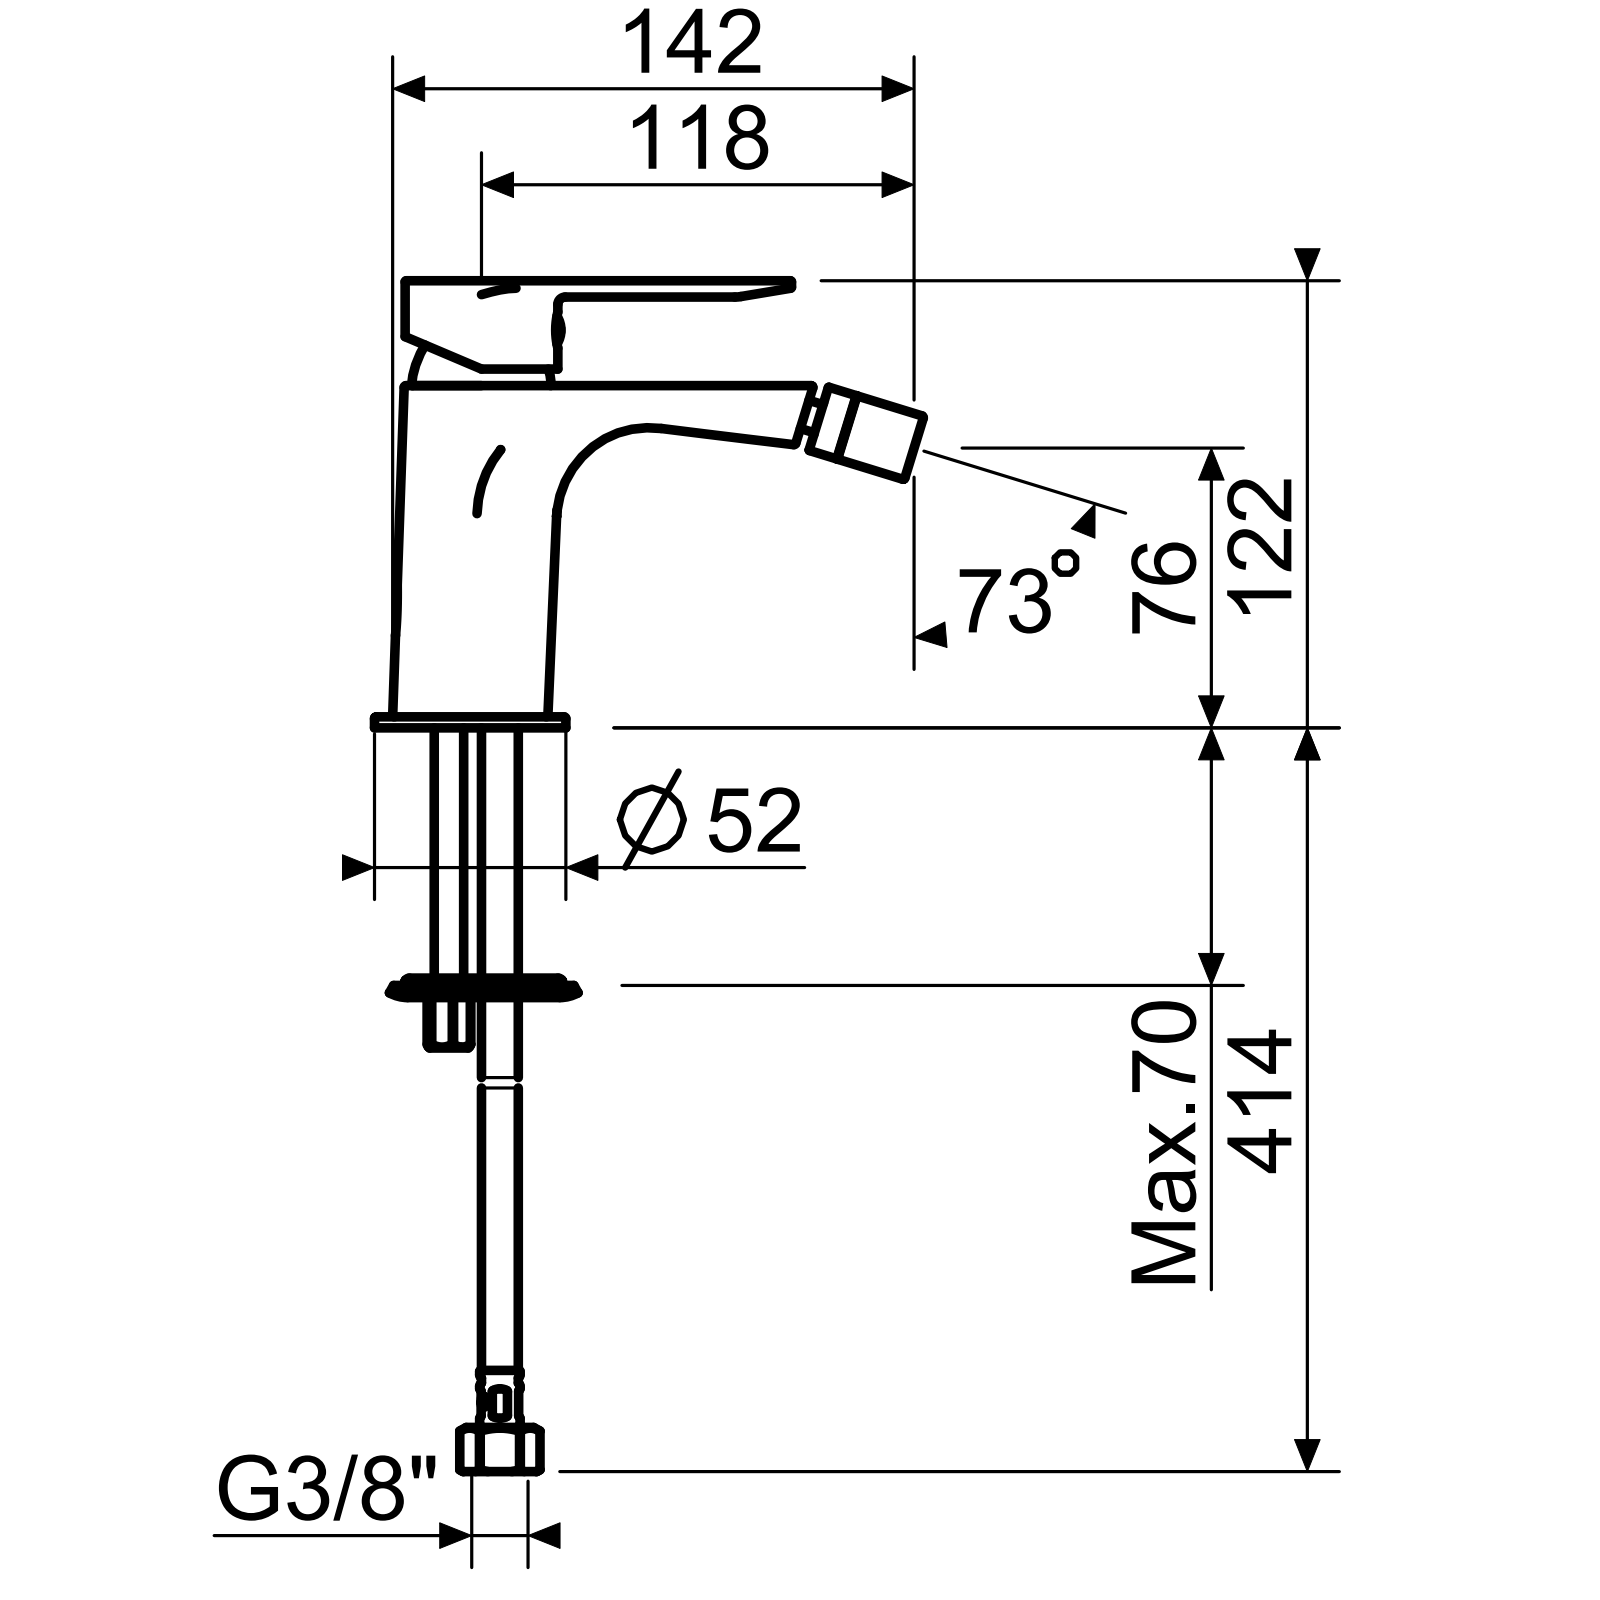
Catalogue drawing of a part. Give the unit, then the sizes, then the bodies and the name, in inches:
Units: inches
Overall size (bounding box): 5.872 × 4.783 × 2.047
Round holes (diameter × count): ⌀0.079 ×2, ⌀0.205 ×2, ⌀0.157 ×1, ⌀0.173 ×1, ⌀0.217 ×1, ⌀0.276 ×1, ⌀0.307 ×1, ⌀0.386 ×1, ⌀0.433 ×1, ⌀0.472 ×1, ⌀0.492 ×1, ⌀0.512 ×1
Round bosses / shafts (diameter × count): ⌀2.047 ×1, ⌀1.634 ×1, ⌀1.496 ×1, ⌀0.709 ×1, ⌀0.63 ×1, ⌀0.594 ×1, ⌀0.591 ×1, ⌀0.524 ×1
Partial cylindrical surfaces — rounded edges, fillets, slot ends (radius × count): R0.012 ×6, R0.02 ×4, R0.197 ×4, R0.394 ×3, R0.079 ×2, R0.222 ×1, R0.276 ×1
Main face-to-face distances: 1.122, 0.087, 1.209, 0.079, 1.13, 1.043, 3.457, 3.543, 4.587, 4.665
Hole centre spacings: 0.079, 0.055, 0.094, 0.099, 0.121, 0.158
Volume: 3.5 in³ · Surface area: 99.05 in²
Bodies: 9 solids, 869 faces (571 planar, 156 cylindrical, 142 other)
Part name (STEP PRODUCT): TOM1904B93ECPCD_1; TOM1904B93ECPCD_2; TOM1904B93ECPCD_3; TOM1904B93ECPCD_6 (+7 more)
STEP written by: CREO PARAMETRIC BY PTC INC, 2020281 (CONFIG_CONTROL_DESIGN)
